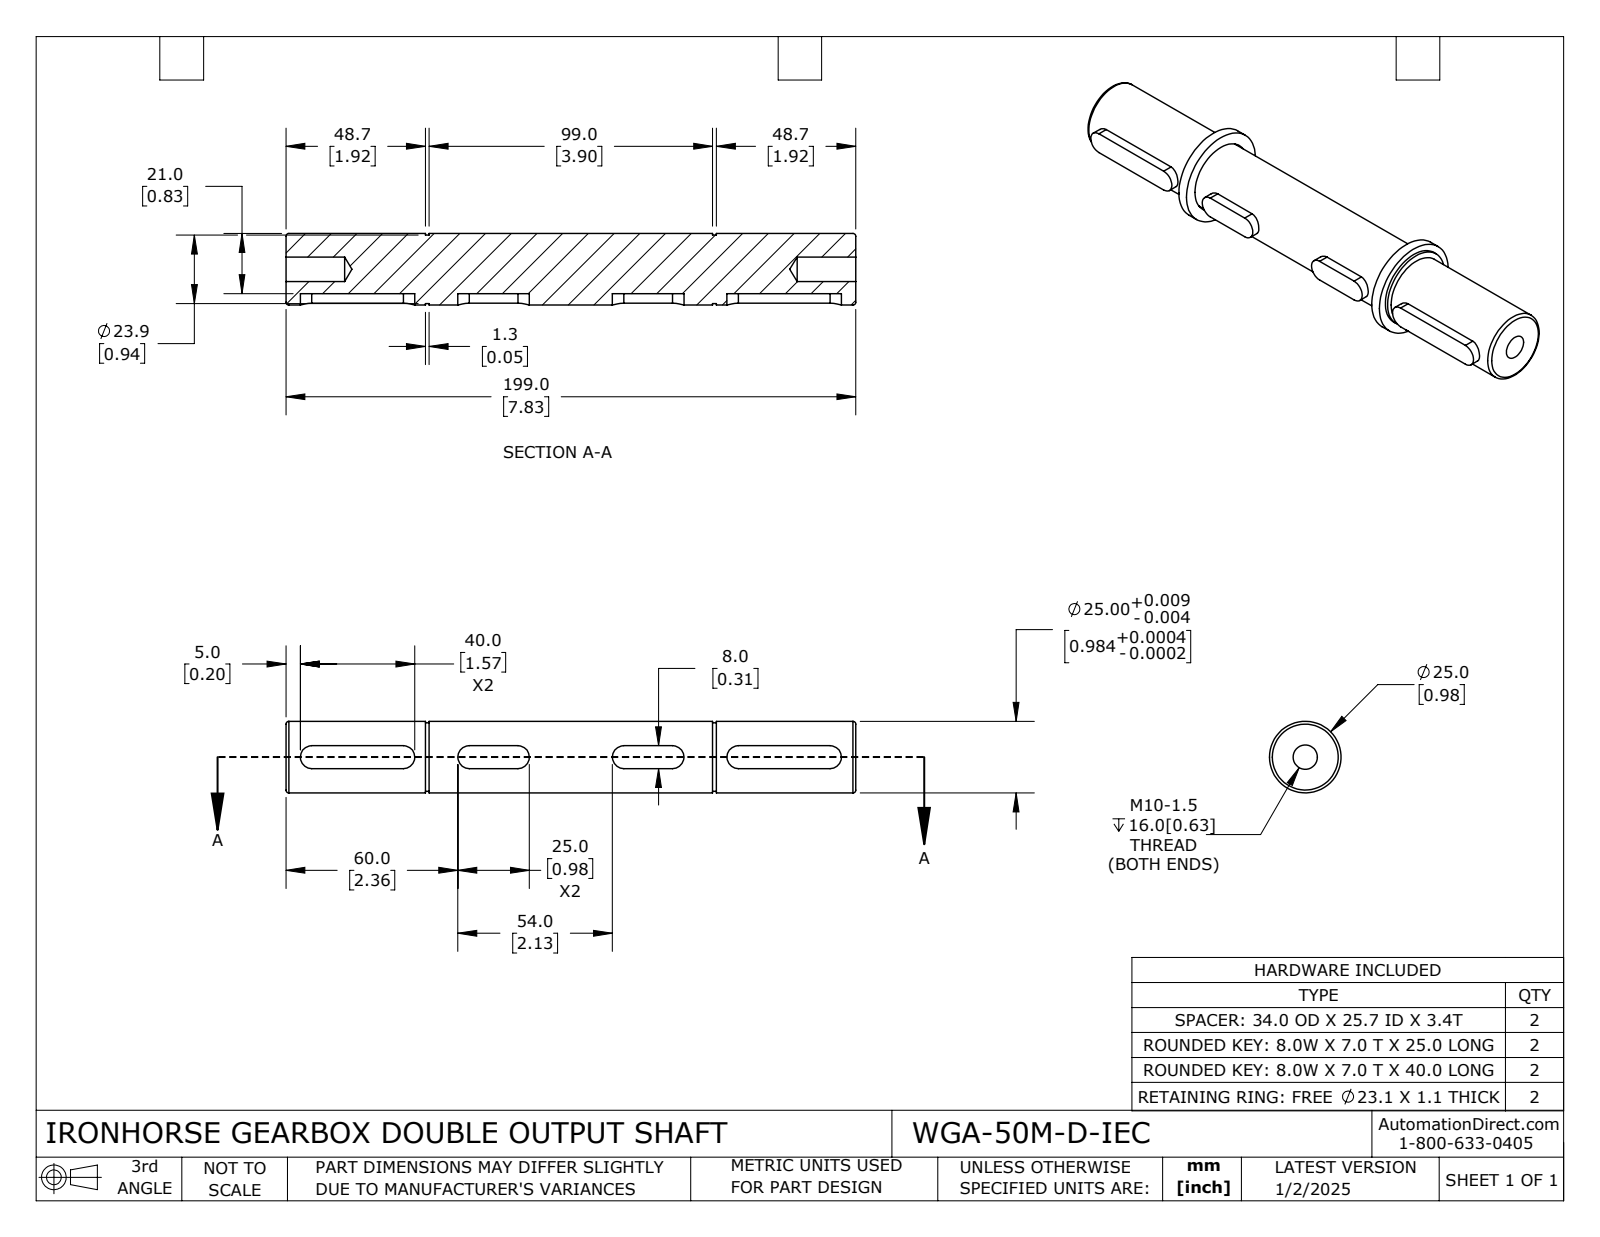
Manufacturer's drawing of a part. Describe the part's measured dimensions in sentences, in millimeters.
The part is named "WGA-50M-D-IEC". Its 3-D file was written by "SolidWorks 2024 (CONFIG_CONTROL_DESIGN)". It is 9 solids with 136 faces: 54 planar, 74 cylindrical and 8 other. Overall it measures 199 by 34 by 34 millimeters. Its volume is 101 632 cubic millimeters and its surface area 27 039 square millimeters. Round holes: 2 of diameter 1.9, 1 of diameter 8.5, 1 of diameter 23.5, 1 of diameter 25.7. Round bosses or shafts: 1 of diameter 34, 1 of diameter 28.05, 1 of diameter 25, 1 of diameter 23.9. Partial cylindrical surfaces (rounded edges, fillets, slot ends): 8 of radius 4, 2 of radius 0.5, 2 of radius 2.5. The main face-to-face distances are 8, 7, 3.75, 95.25, 50, 53.75, 145.25, 149, 99, 48.9. The hole center spacings are 14.23, 3.
